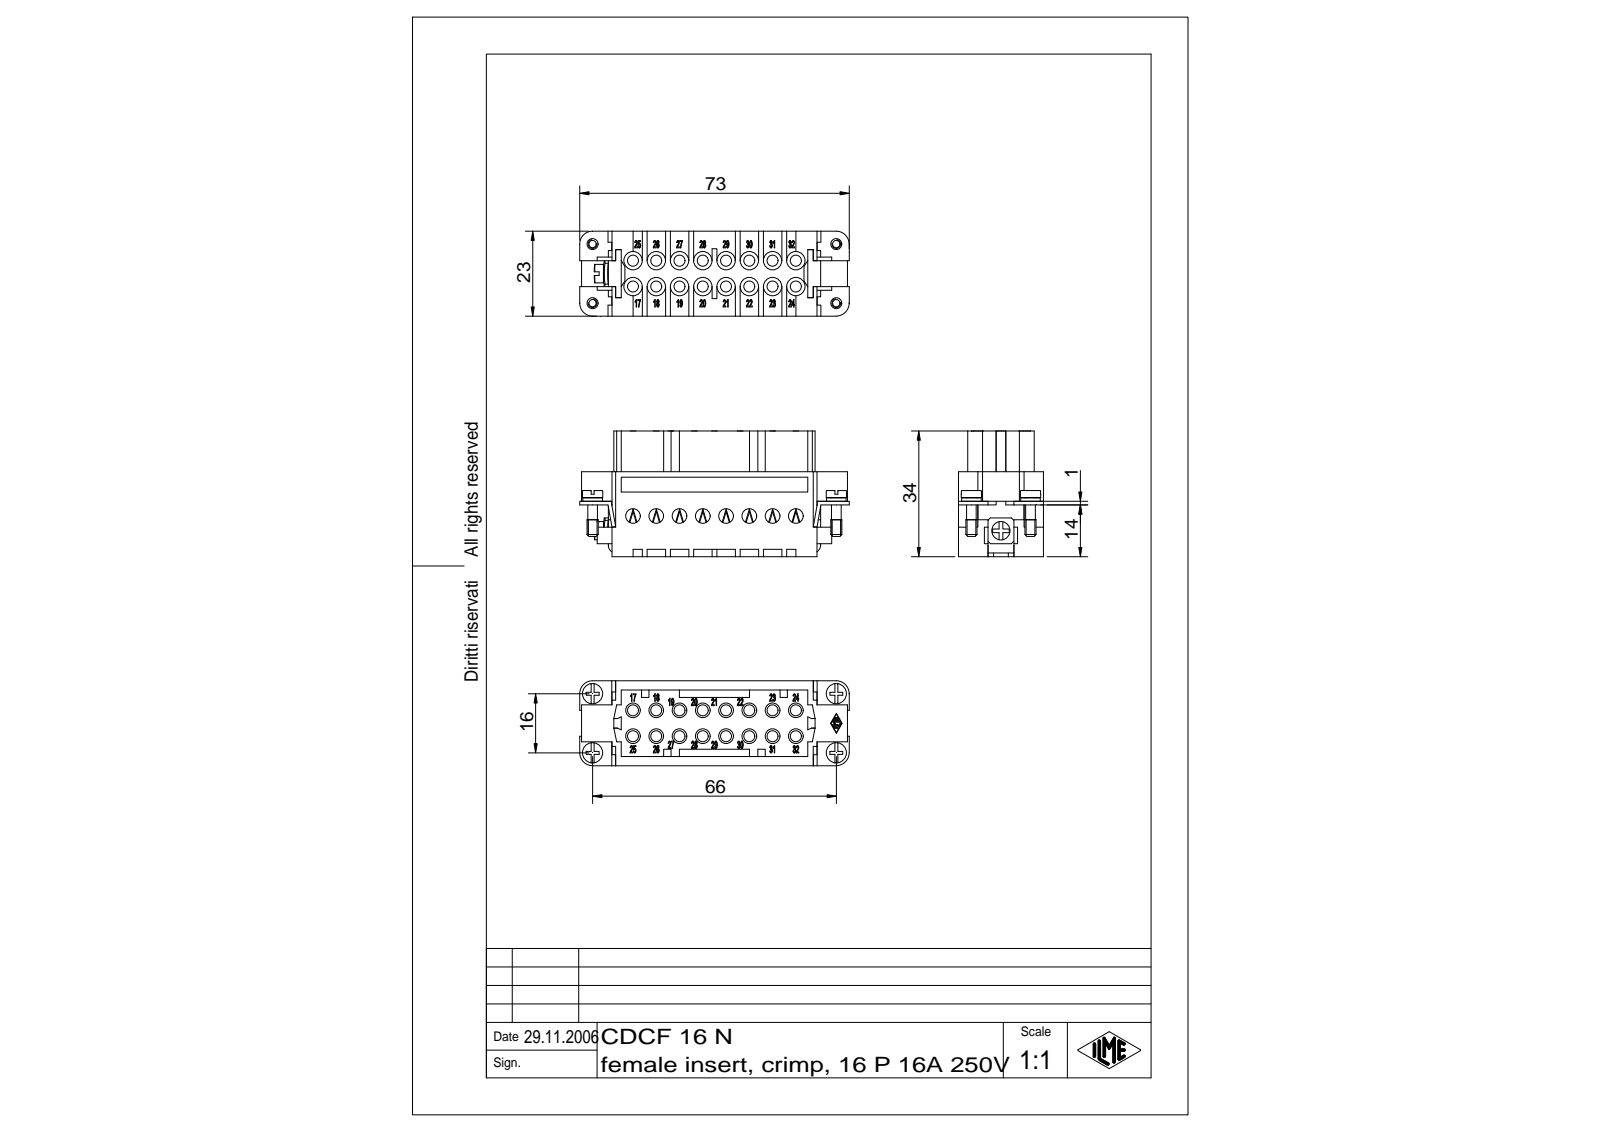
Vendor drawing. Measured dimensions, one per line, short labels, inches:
name: CDCF 16 N
written by: Autodesk Inventor 7 (AUTOMOTIVE_DESIGN)
unit: in
bodies: 17 solids, 1805 faces (705 planar, 152 cylindrical, 948 other)
size: 2.874 × 1.339 × 0.906
volume: 1.859 in³; area: 30.25 in²
holes: 16× ⌀0.157, 8× ⌀0.118, 8× ⌀0.197, 1× ⌀0.128
bosses: 2× ⌀0.217, 2× ⌀0.209, 2× ⌀0.118, 2× ⌀0.102, 1× ⌀0.197
rounds: 14× R0.004, 2× R0.039, 2× R0.079, 2× R0.138, 1× R0.177
face distances: 0.079, 0.906, 0.098, 0.551, 0.315, 0.059, 0.807, 0.157, 0.177, 0.63
hole spacings: 0.248, 0.496, 0.744, 0.992, 1.24, 1.488, 1.736
